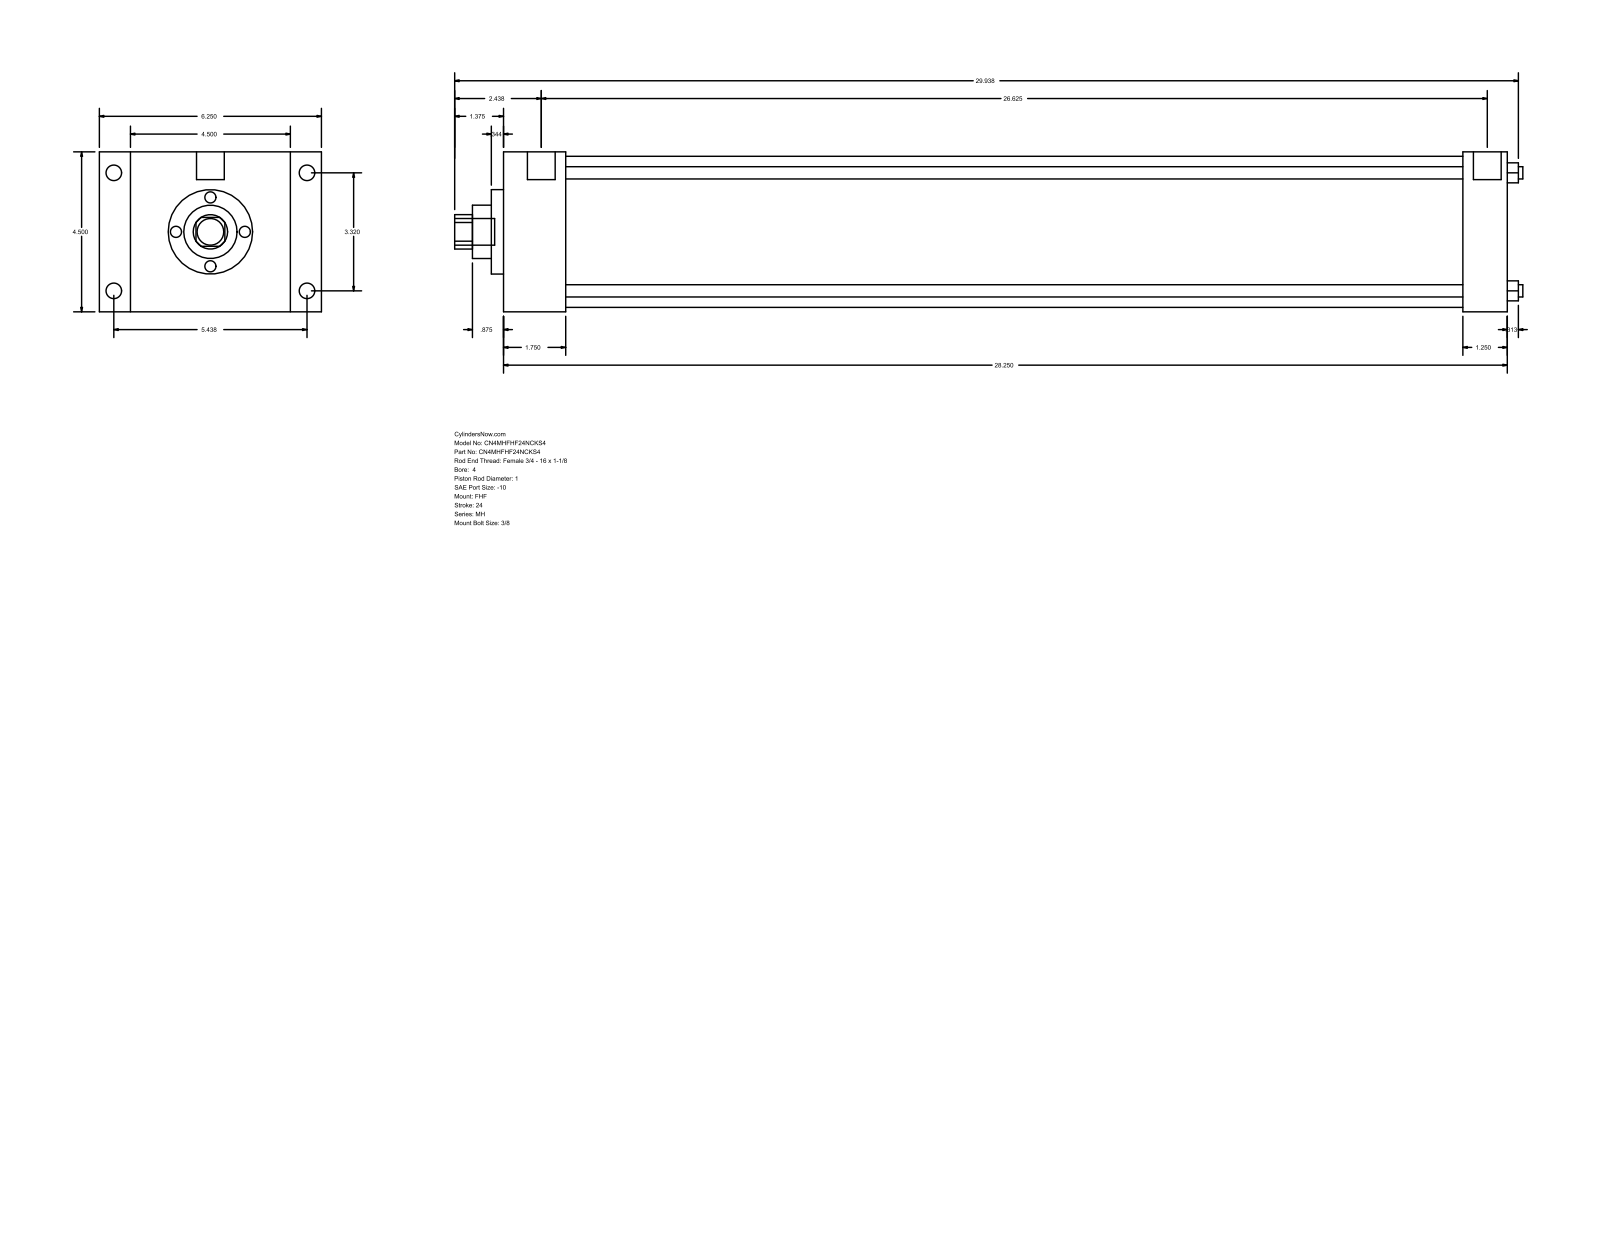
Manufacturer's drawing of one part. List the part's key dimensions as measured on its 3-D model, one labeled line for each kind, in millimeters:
Part name (STEP PRODUCT): MH_FHF__0400_1
STEP written by: GSSL Pune (CONFIG_CONTROL_DESIGN)
Units: millimetres
Bodies: 0 solids, 90 faces (61 planar, 29 cylindrical, 0 other)
Overall size (bounding box): 763.59 × 158.75 × 114.3
Round holes (diameter × count): ⌀8.76 ×4, ⌀25.4 ×1, ⌀38.1 ×1, ⌀60.33 ×1, ⌀107.95 ×1
Round bosses / shafts (diameter × count): ⌀11.13 ×4, ⌀8.73 ×4, ⌀19.84 ×2, ⌀19.05 ×1
Partial cylindrical surfaces — rounded edges, fillets, slot ends (radius × count): R12.29 ×1
Main face-to-face distances: 114.3, 717.56, 44.46, 673.1, 22.23, 136.53, 158.76, 685.81, 641.35, 31.75
Hole centre spacings: 59.62, 84.32, 119.25
